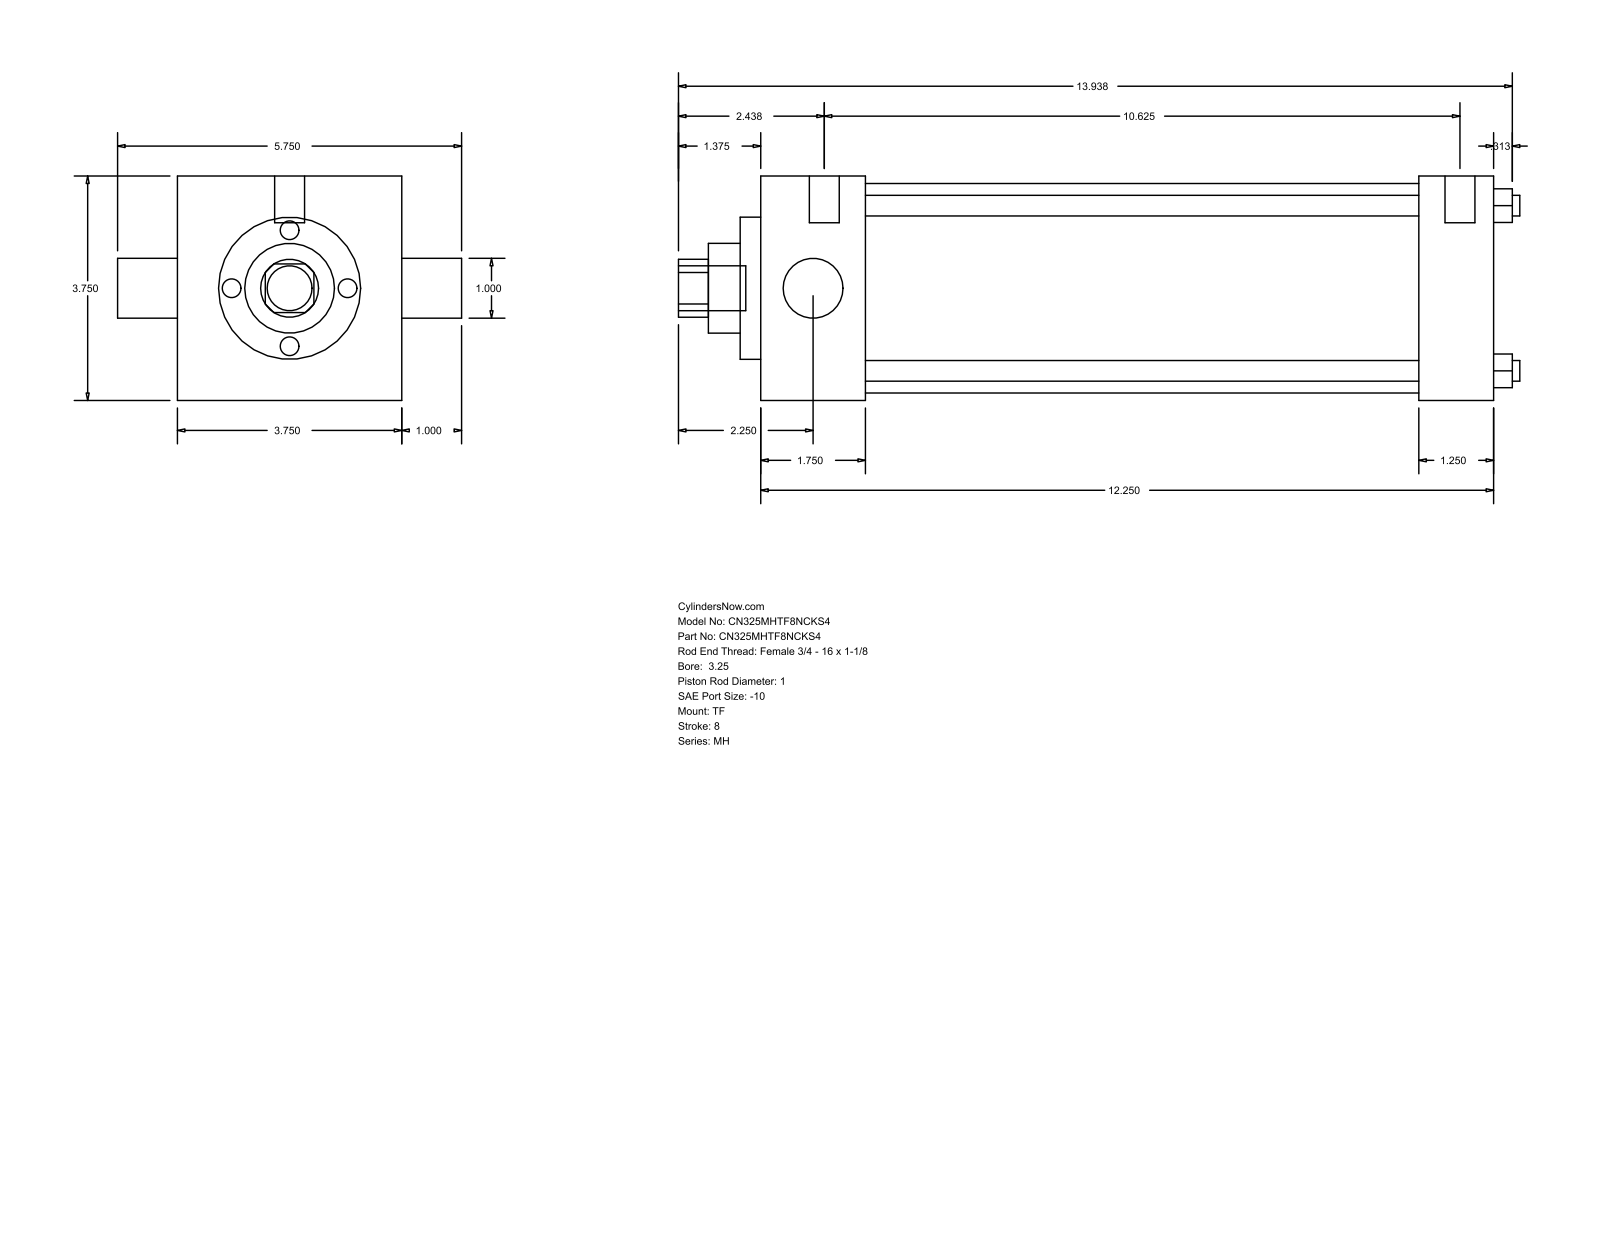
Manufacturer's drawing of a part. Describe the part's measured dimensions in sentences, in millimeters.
The part is named "MH_TF__0325_1". Its 3-D file was written by "GSSL Pune (CONFIG_CONTROL_DESIGN)". It is 0 solids with 86 faces: 61 planar, 25 cylindrical and 0 other. Overall it measures 357.19 by 146.05 by 95.25 millimeters. Round holes: 4 of diameter 8.76, 2 of diameter 25.4, 1 of diameter 38.1, 1 of diameter 60.33, 1 of diameter 88.9. Round bosses or shafts: 3 of diameter 5.56, 2 of diameter 12.7, 1 of diameter 19.05. Partial cylindrical surfaces (rounded edges, fillets, slot ends): 1 of radius 12.29. The main face-to-face distances are 95.24, 311.15, 44.46, 279.4, 234.94, 266.69, 31.75, 8.73, 53.19, 288.13. The hole center spacings are 49.57, 70.1, 99.14.
